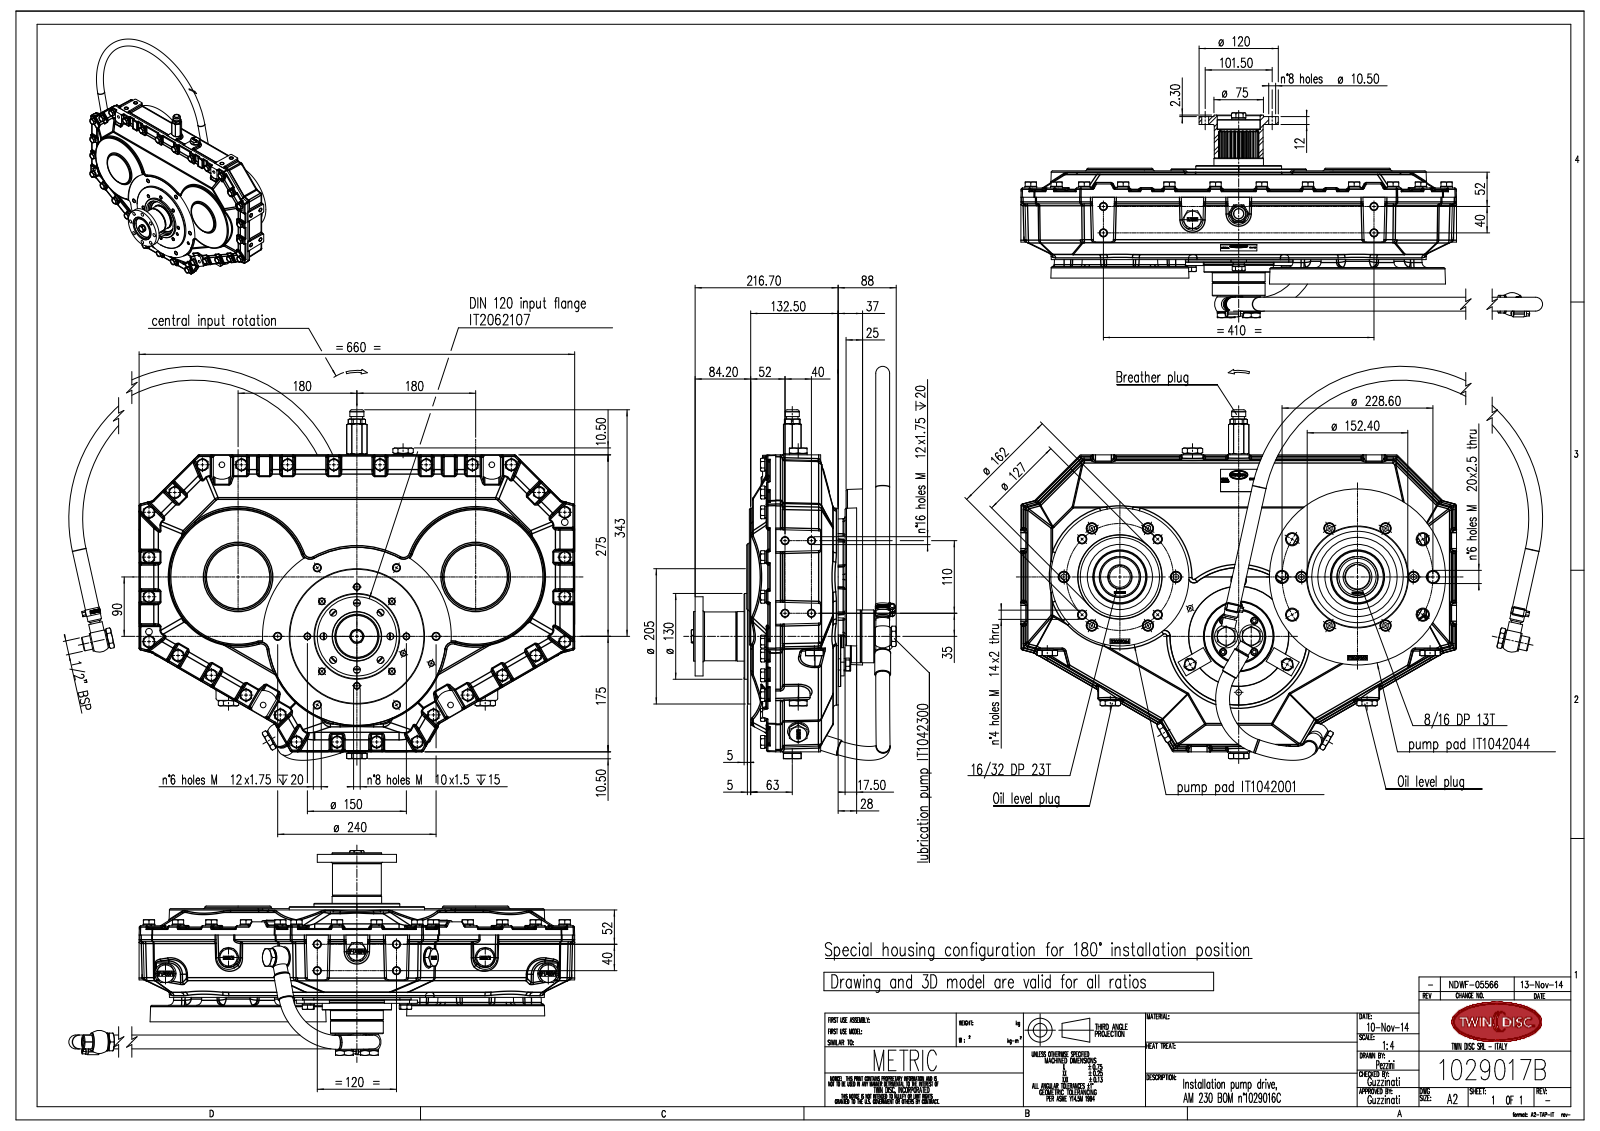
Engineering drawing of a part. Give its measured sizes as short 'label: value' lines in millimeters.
name: IT4588040_rev00-installation; ITam230-001_rev01-installation; 1029017B; ITam450-002_rev00-installation (+8 more)
written by: SolidWorks 2007 (AUTOMOTIVE_DESIGN)
unit: mm
bodies: 45 solids, 9148 faces (3481 planar, 2743 cylindrical, 2924 other)
size: 806.43 × 596.95 × 310.5
volume: 3 821 000 mm³; area: 2 826 000 mm²
holes: 52× ⌀10.2, 38× ⌀10.5, 30× ⌀8.5, 23× ⌀12, 21× ⌀11, 13× ⌀21, 12× ⌀17, 10× ⌀8, 10× ⌀10, 10× ⌀13, 6× ⌀5, 6× ⌀7
bosses: 51× ⌀10, 33× ⌀18.1, 33× ⌀16.2, 12× ⌀16, 9× ⌀27, 6× ⌀20, 6× ⌀6, 5× ⌀18
rounds: 201× R2, 115× R3, 78× R2.5, 74× R5, 58× R0.45, 18× R1.5, 18× R13, 12× R8
face distances: 21, 5, 40, 4, 94.5, 19, 115.5, 26, 141.5, 8
hole spacings: 35.96, 38.84, 60.82, 78.12, 93.78, 40, 85, 17.25
